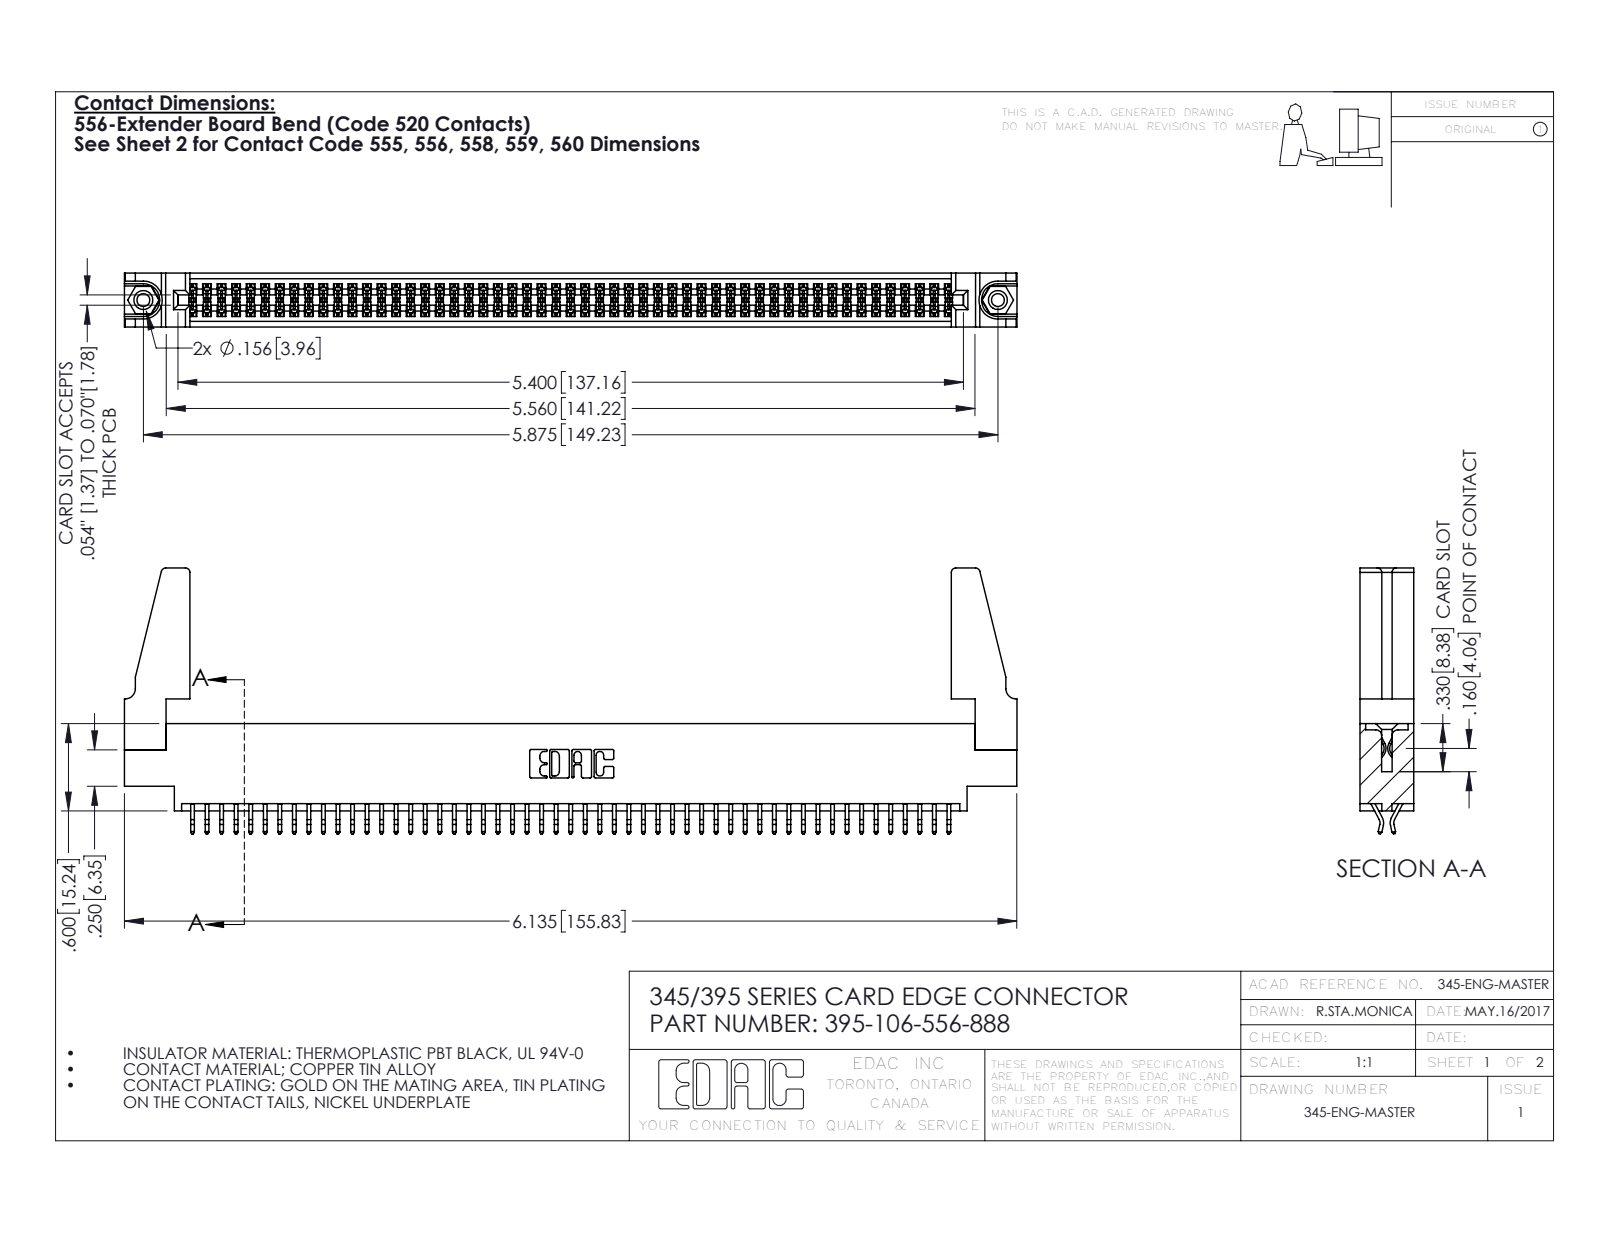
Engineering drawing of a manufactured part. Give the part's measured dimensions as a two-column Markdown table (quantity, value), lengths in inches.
| quantity | value |
| --- | --- |
| part name | 345 Part_0.170 Offset - 0.156 Dia-TH; 345-292-001_556 Tail; 345-250-001_345-250-001-102; 395-106-556-888 (+1 more) |
| STEP written by | SolidWorks 2016 (CONFIG_CONTROL_DESIGN) |
| units | inches |
| bodies | 111 solids, 6190 faces (4078 planar, 2096 cylindrical, 16 other) |
| overall size | 6.136 × 1.827 × 0.37 |
| volume | 1.121 in³ |
| surface area | 39.9 in² |
| round holes (diameter × count) | 0.089 × 2, 0.125 × 2, 0.156 × 2, 0.064 × 1 |
| round bosses / shafts (diameter × count) | 0.155 × 2 |
| partial cylindrical surfaces (radius × count) | 0.006 × 159, 0.01 × 22, 0.03 × 8, 0.007 × 6, 0.031 × 6, 0.026 × 3, 0.01 × 2, 0.014 × 2 |
| main face-to-face distances | 0.072, 0.298, 0.37, 0.025, 0.2, 0.098, 0.272, 0.225, 0.175, 0.149 |
| hole center spacings | 0.27, 5.639, 5.875 |
